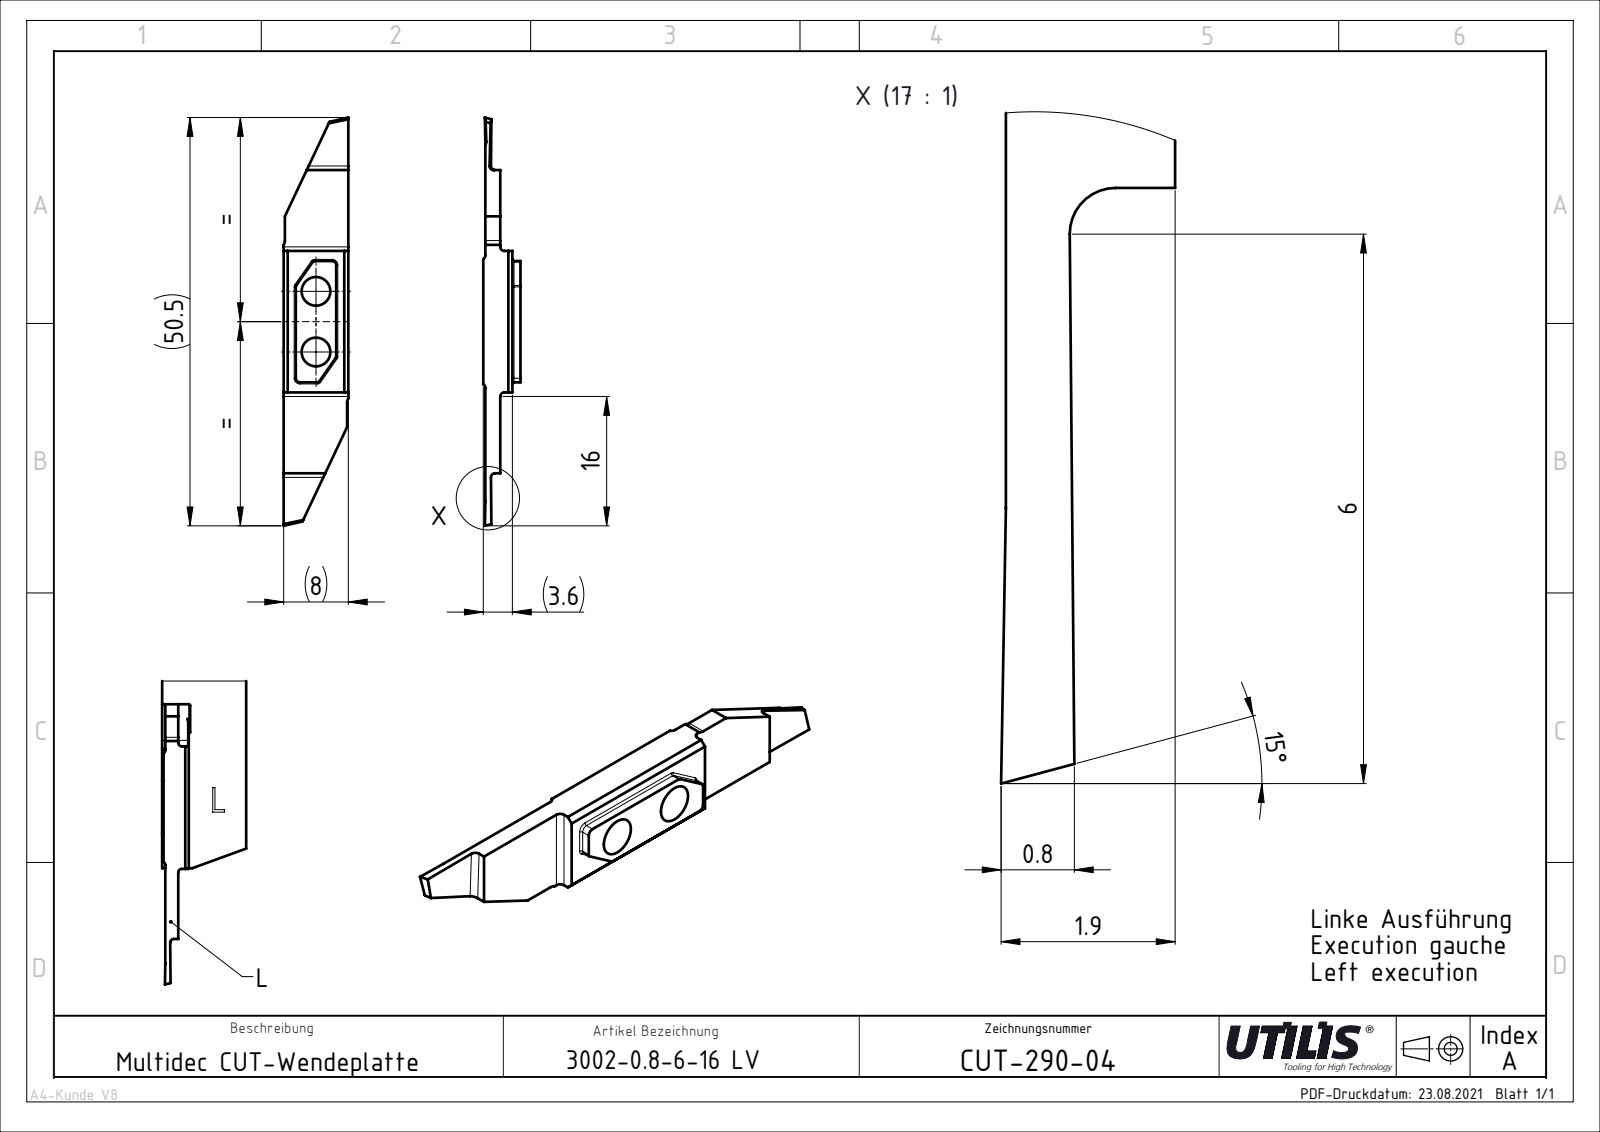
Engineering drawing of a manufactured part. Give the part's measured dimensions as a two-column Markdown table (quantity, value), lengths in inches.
| quantity | value |
| --- | --- |
| part name | CUT-290-04 |
| STEP written by | SolidWorks 2016 (AUTOMOTIVE_DESIGN) |
| units | inches |
| bodies | 1 solid, 38 faces (24 planar, 14 cylindrical, 0 other) |
| overall size | 1.988 × 0.315 × 0.14 |
| volume | 0.044 in³ |
| surface area | 1.46 in² |
| round holes (diameter × count) | 0.14 × 2 |
| partial cylindrical surfaces (radius × count) | 0.02 × 6, 0.006 × 2, 0.039 × 2 |
| main face-to-face distances | 0.073, 0.13, 0.057, 0.083, 0.14, 0.315, 0.713, 0.309, 0.689, 0.303 |
| hole center spacings | 0.295 |
